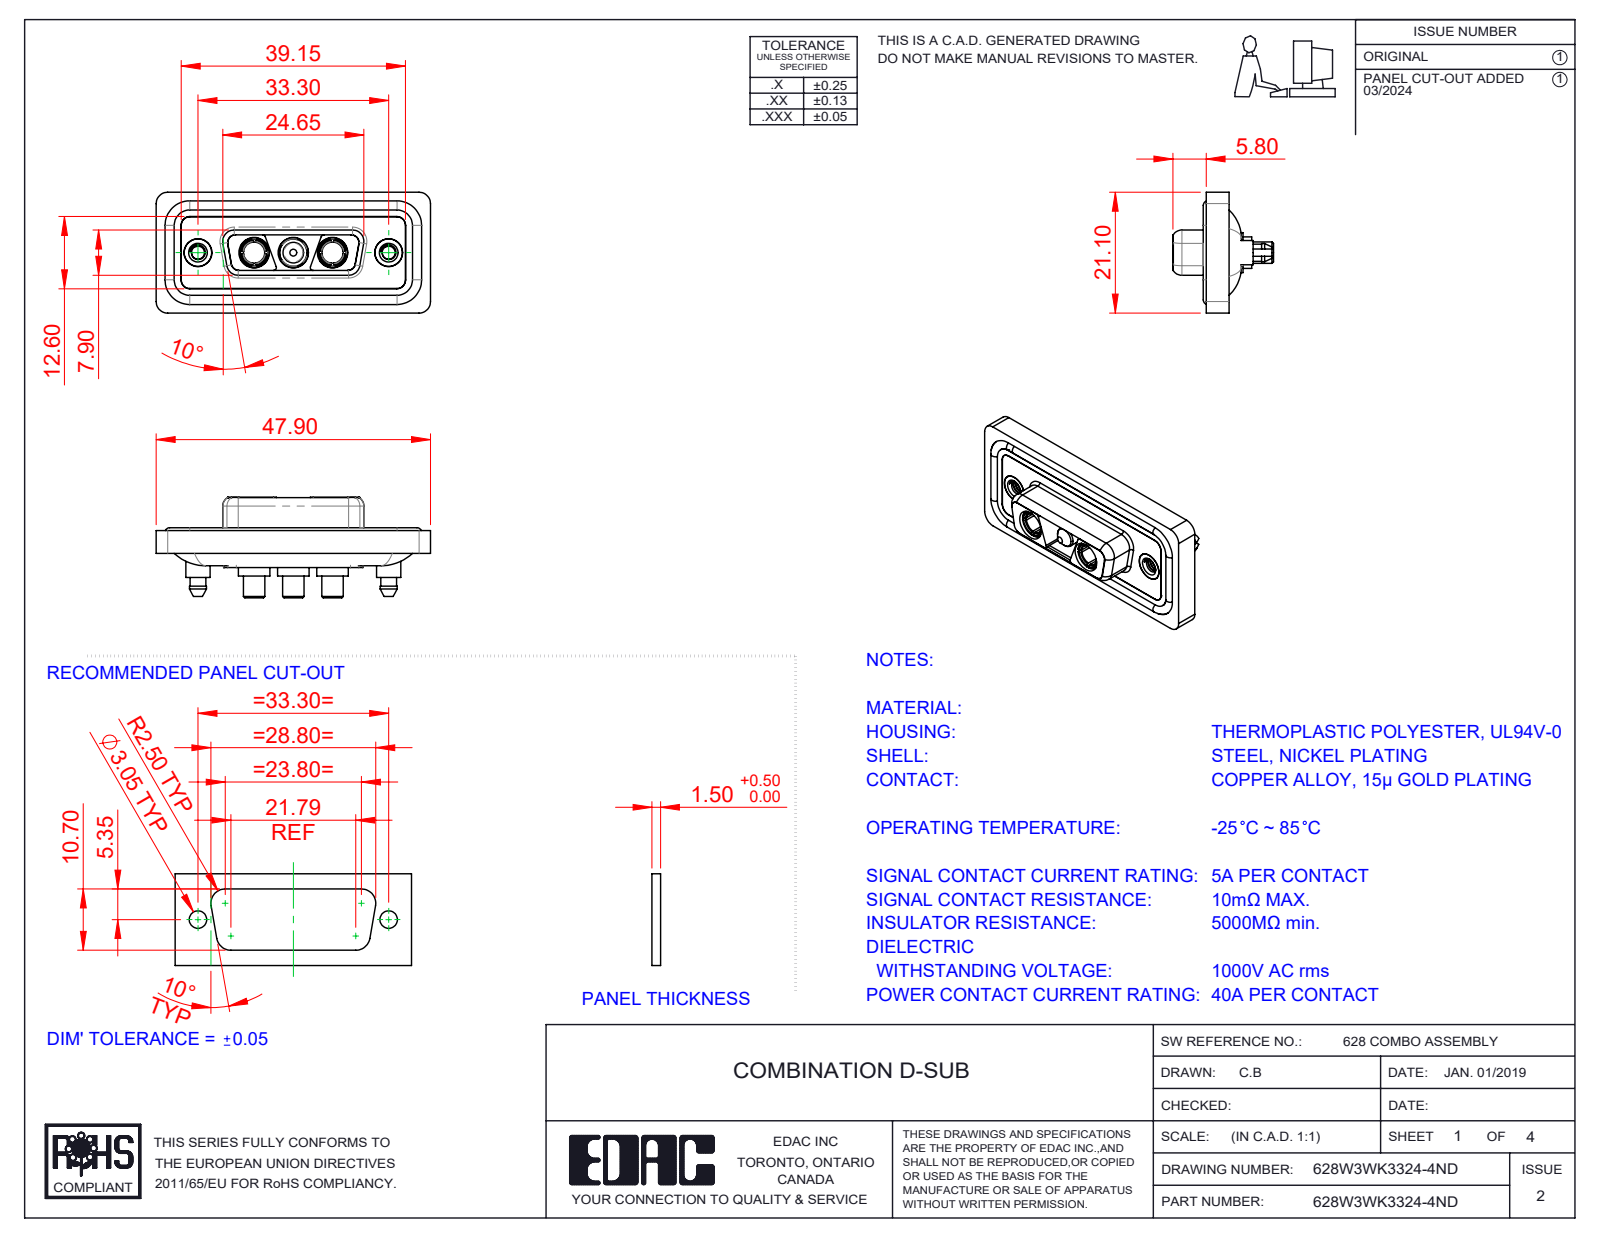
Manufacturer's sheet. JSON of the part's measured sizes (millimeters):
{"part_name": "Power Socket_40A S; 628Combo Housing_3WK3; 628Combo Waterproof Housing_15 Contacts; 628Combo Shell Rear_15 Contacts (+4 more)", "step_written_by": "SolidWorks 2023 (CONFIG_CONTROL_DESIGN)", "units": "millimeters", "bodies": {"solids": 13, "faces": 649, "planar": 194, "cylindrical": 306, "other": 149}, "overall_size": [47.9, 21.1, 17.55], "volume_mm3": 6069, "surface_area_mm2": 9877, "round_holes": [[4.85, 5], [5.3, 3], [2.26, 2], [3.7, 2], [4, 2], [4.05, 2], [5, 2]], "round_bosses_or_shafts": [[1.6, 4], [5.5, 3], [5.2, 3], [4.75, 3], [3.75, 3], [5.4, 2], [4.96, 2], [4.95, 2]], "partial_cylinders_radius": [[1.5, 24], [2, 20], [1.35, 12], [1.6, 10], [0.5, 8], [0.25, 4], [0.6, 4], [0.65, 4]], "face_to_face_distances": [0.4, 1.6, 0.5, 1.8, 1.1, 2.9, 5.65, 7.05, 5.35, 1.5], "hole_center_spacings": [6.85, 9.8, 16.65, 23.5, 13.7, 33.3]}
